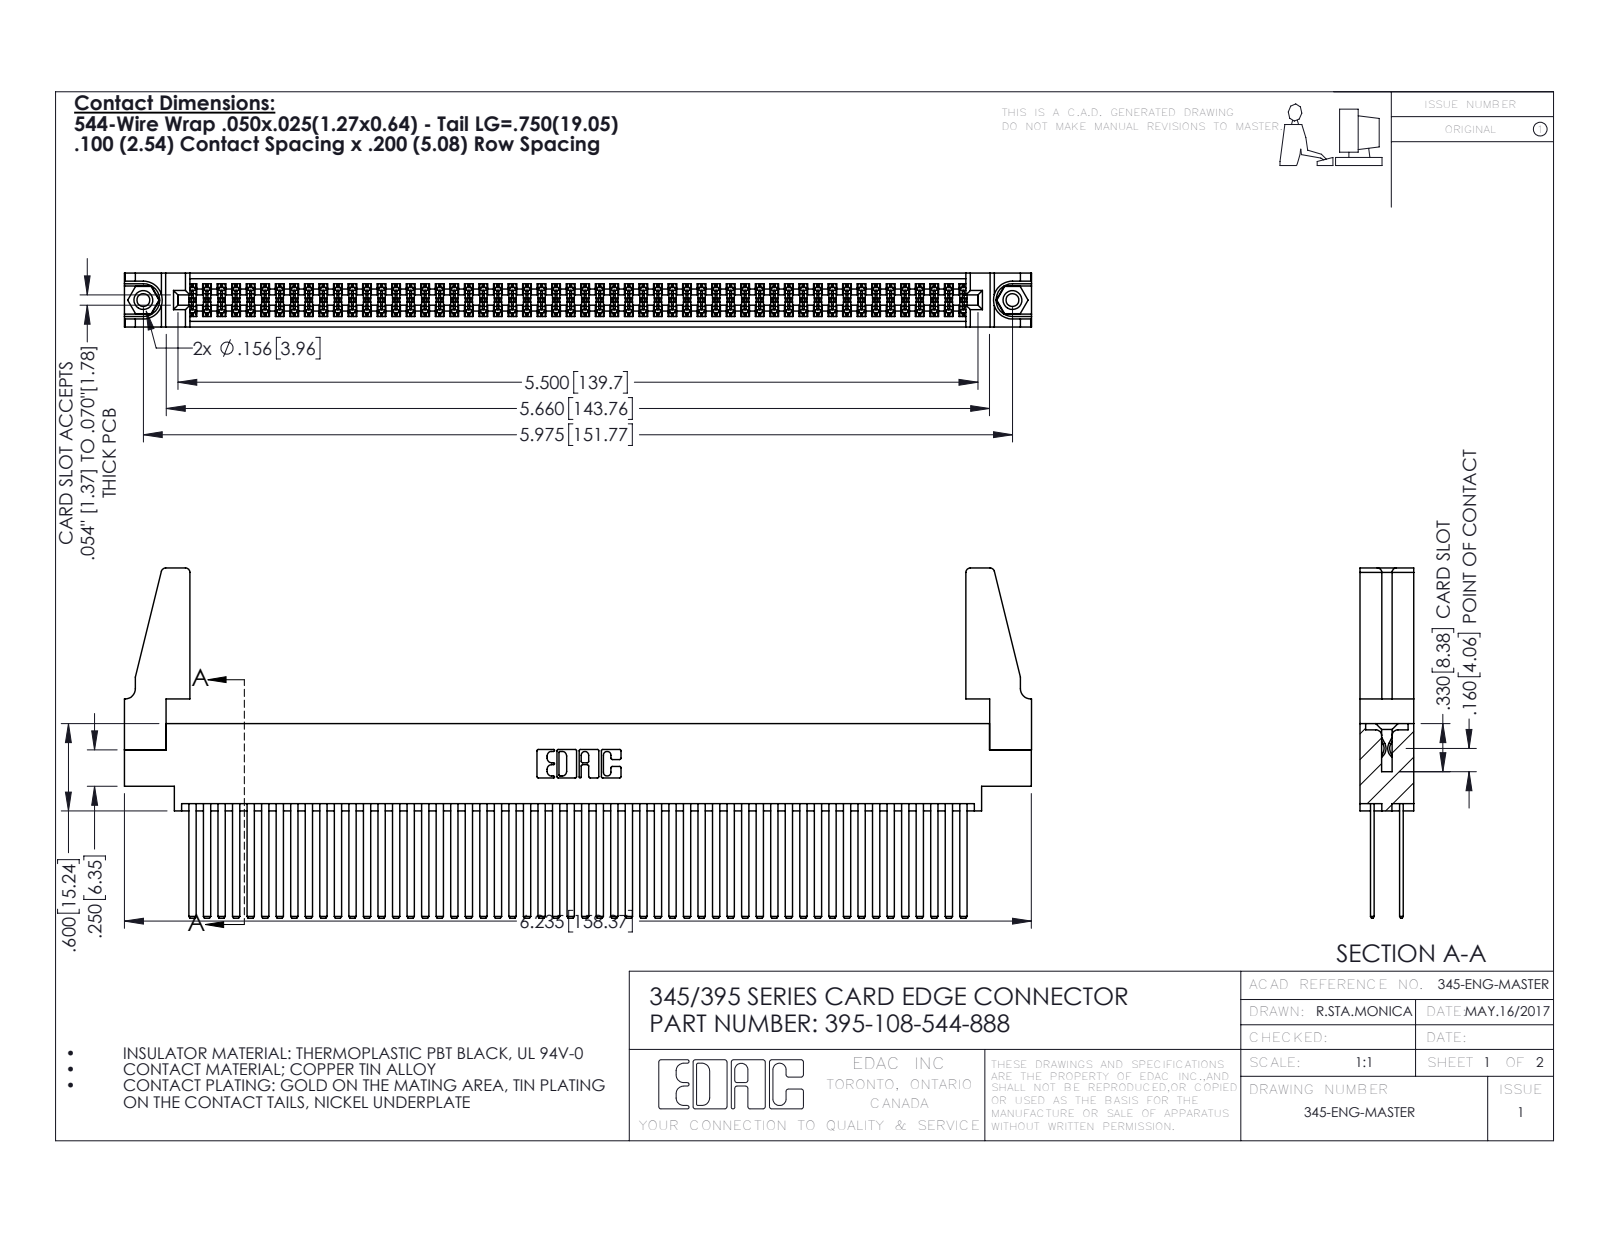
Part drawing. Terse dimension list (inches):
name: 345 Part_0.170 Offset - 0.156 Dia-TH; 395-108-544-888; 345-220-078_345-220-088; 345-292-001_345-293-144 (+1 more)
written by: SolidWorks 2016 (CONFIG_CONTROL_DESIGN)
unit: in
bodies: 113 solids, 5006 faces (3288 planar, 1702 cylindrical, 16 other)
size: 6.236 × 2.407 × 0.37
volume: 1.23 in³; area: 51.02 in²
holes: 2× ⌀0.089, 2× ⌀0.125, 2× ⌀0.156, 1× ⌀0.064
bosses: 2× ⌀0.155
rounds: 162× R0.006, 22× R0.01, 8× R0.03, 6× R0.007, 6× R0.031, 3× R0.026, 2× R0.014, 2× R0.019
face distances: 0.072, 0.298, 0.2, 0.098, 0.272, 0.025, 0.225, 0.37, 0.175, 0.149
hole spacings: 0.27, 5.739, 5.975
